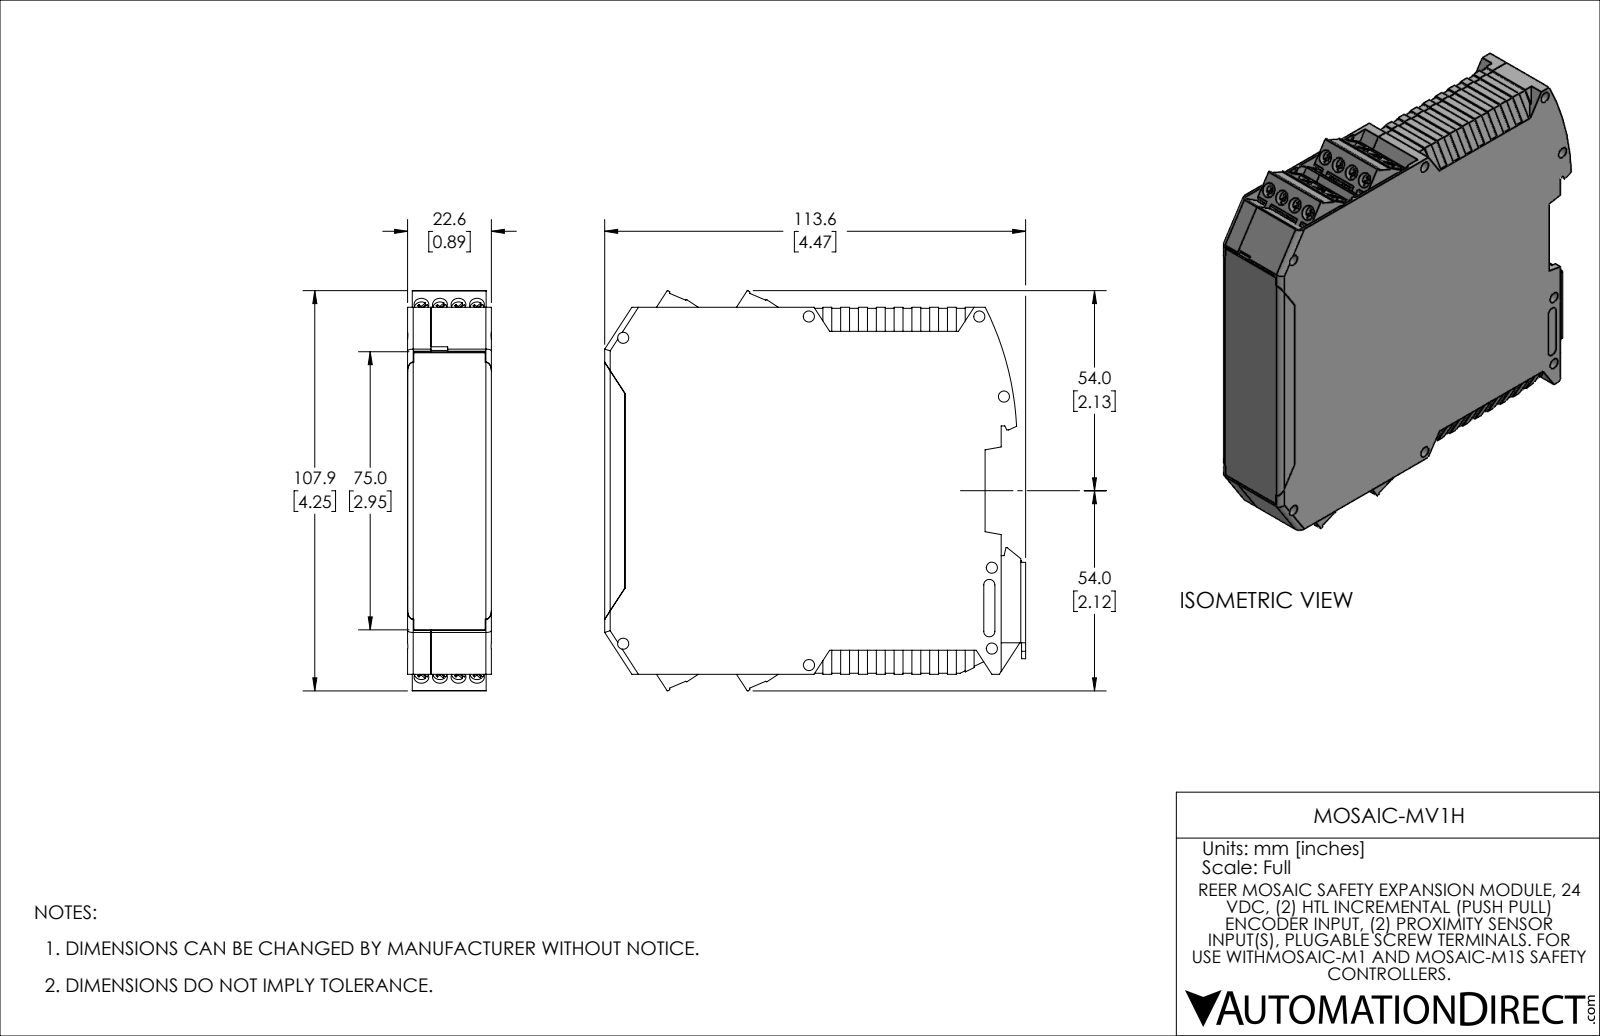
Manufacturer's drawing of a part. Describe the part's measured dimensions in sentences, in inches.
The part is named "MOSAIC-MV1H". Its 3-D file was written by "SolidWorks 2021 (AUTOMOTIVE_DESIGN)". It is 9 solids with 1954 faces: 1569 planar, 379 cylindrical and 6 other. Overall it measures 4.472 by 4.25 by 0.89 inches. Its volume is 3.484 cubic inches and its surface area 117.5 square inches. Round holes: 18 of diameter 0.055, 16 of diameter 0.11, 16 of diameter 0.157, 14 of diameter 0.118, 1 of diameter 0.063. Round bosses or shafts: 16 of diameter 0.149, 1 of diameter 0.177, 1 of diameter 0.11, 1 of diameter 0.053. Partial cylindrical surfaces (rounded edges, fillets, slot ends): 33 of radius 0.012, 16 of radius 0.114, 12 of radius 0.008, 12 of radius 0.03, 8 of radius 0.059, 6 of radius 0.031, 5 of radius 0.098, 4 of radius 0.024. The main face-to-face distances are 0.049, 0.841, 0.89, 0.791, 0.039, 0.248, 0.047, 0.199, 0.593, 0.642. The hole center spacings are 0.197, 0.394, 0.591, 0.503, 0.504, 0.74, 0.74, 0.463.
